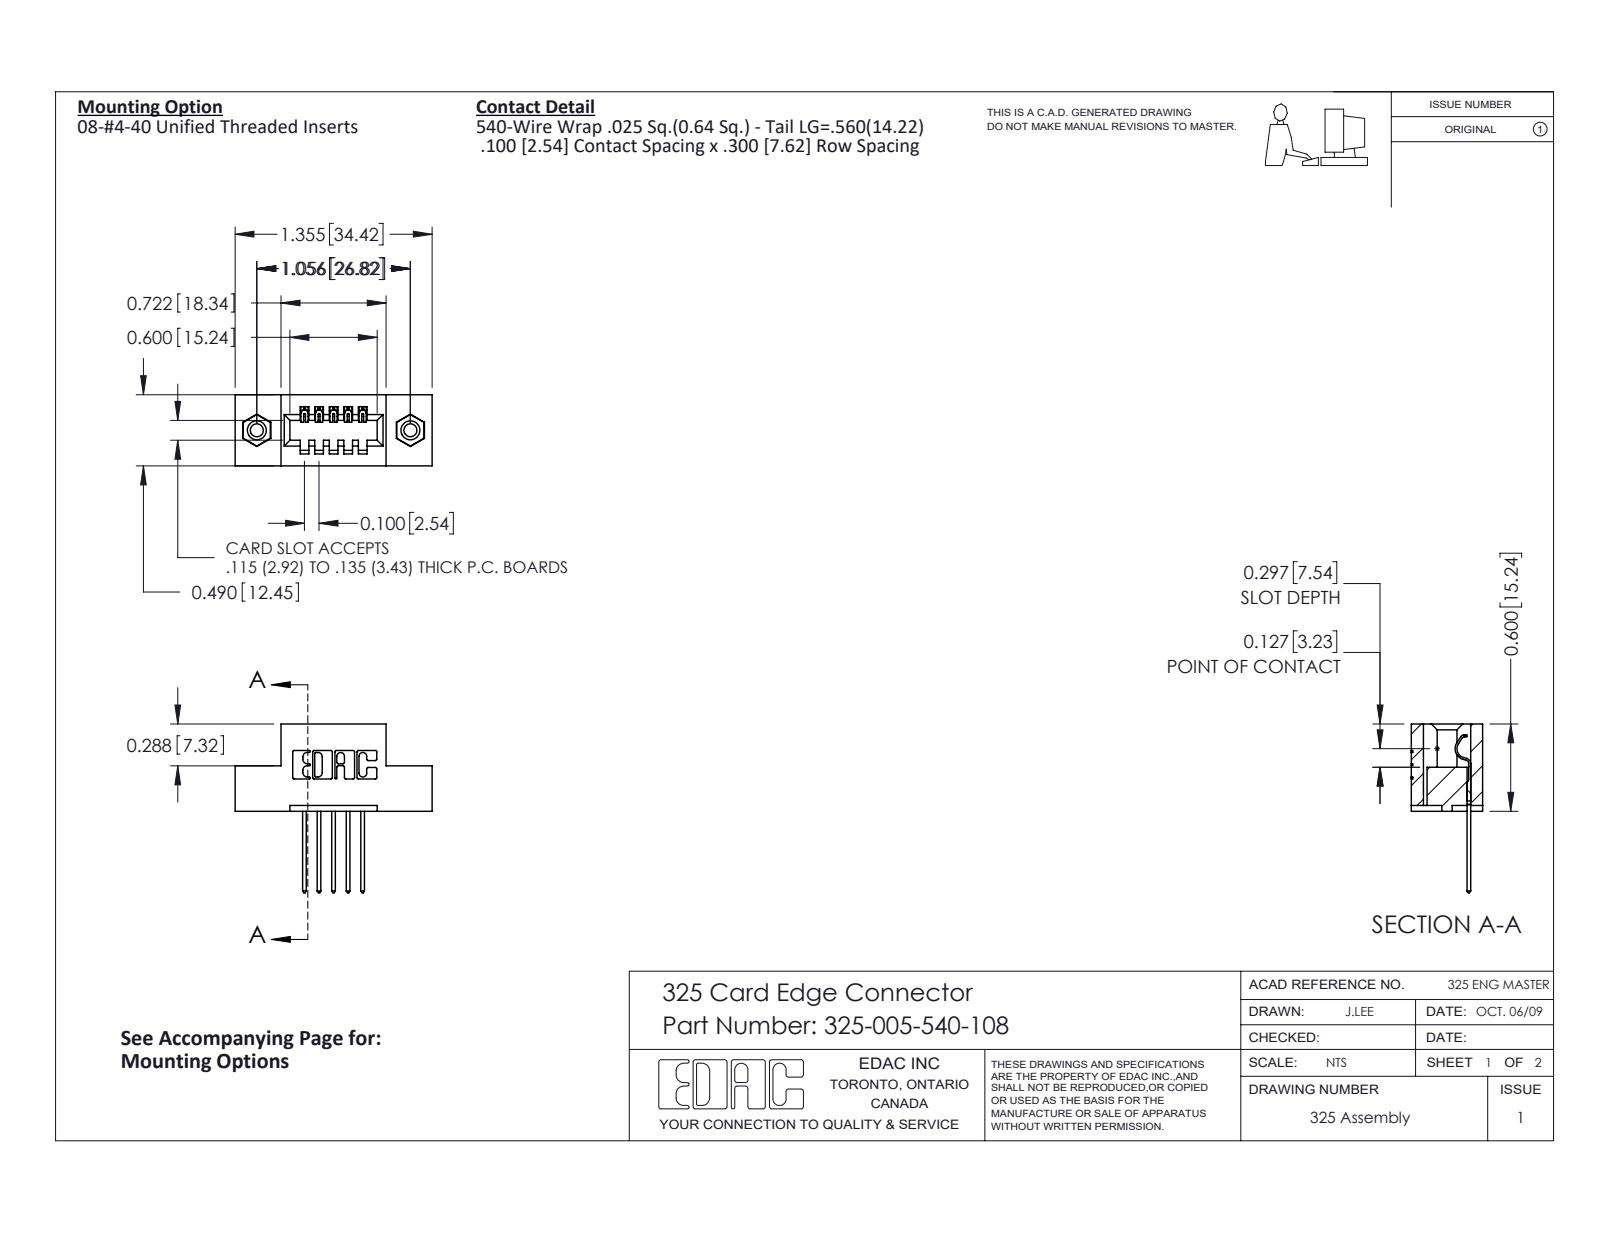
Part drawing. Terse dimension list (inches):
name: 325-292-001_325-293-140; 325 Part_TI; 345-250-001_345-250-003-102; 325-005-540-108
written by: SolidWorks 2016 (CONFIG_CONTROL_DESIGN)
unit: in
bodies: 8 solids, 464 faces (312 planar, 136 cylindrical, 16 other)
size: 1.355 × 1.16 × 0.49
volume: 0.249 in³; area: 6.035 in²
holes: 2× ⌀0.089, 2× ⌀0.125, 2× ⌀0.16
bosses: 2× ⌀0.155
rounds: 22× R0.01, 10× R0.006, 10× R0.01, 6× R0.007, 6× R0.031, 3× R0.026, 1× R0.014, 1× R0.022
face distances: 0.1, 0.49, 0.3, 0.083, 0.04, 0.407, 0.2, 0.06, 0.317, 1.039
hole spacings: 1.056
